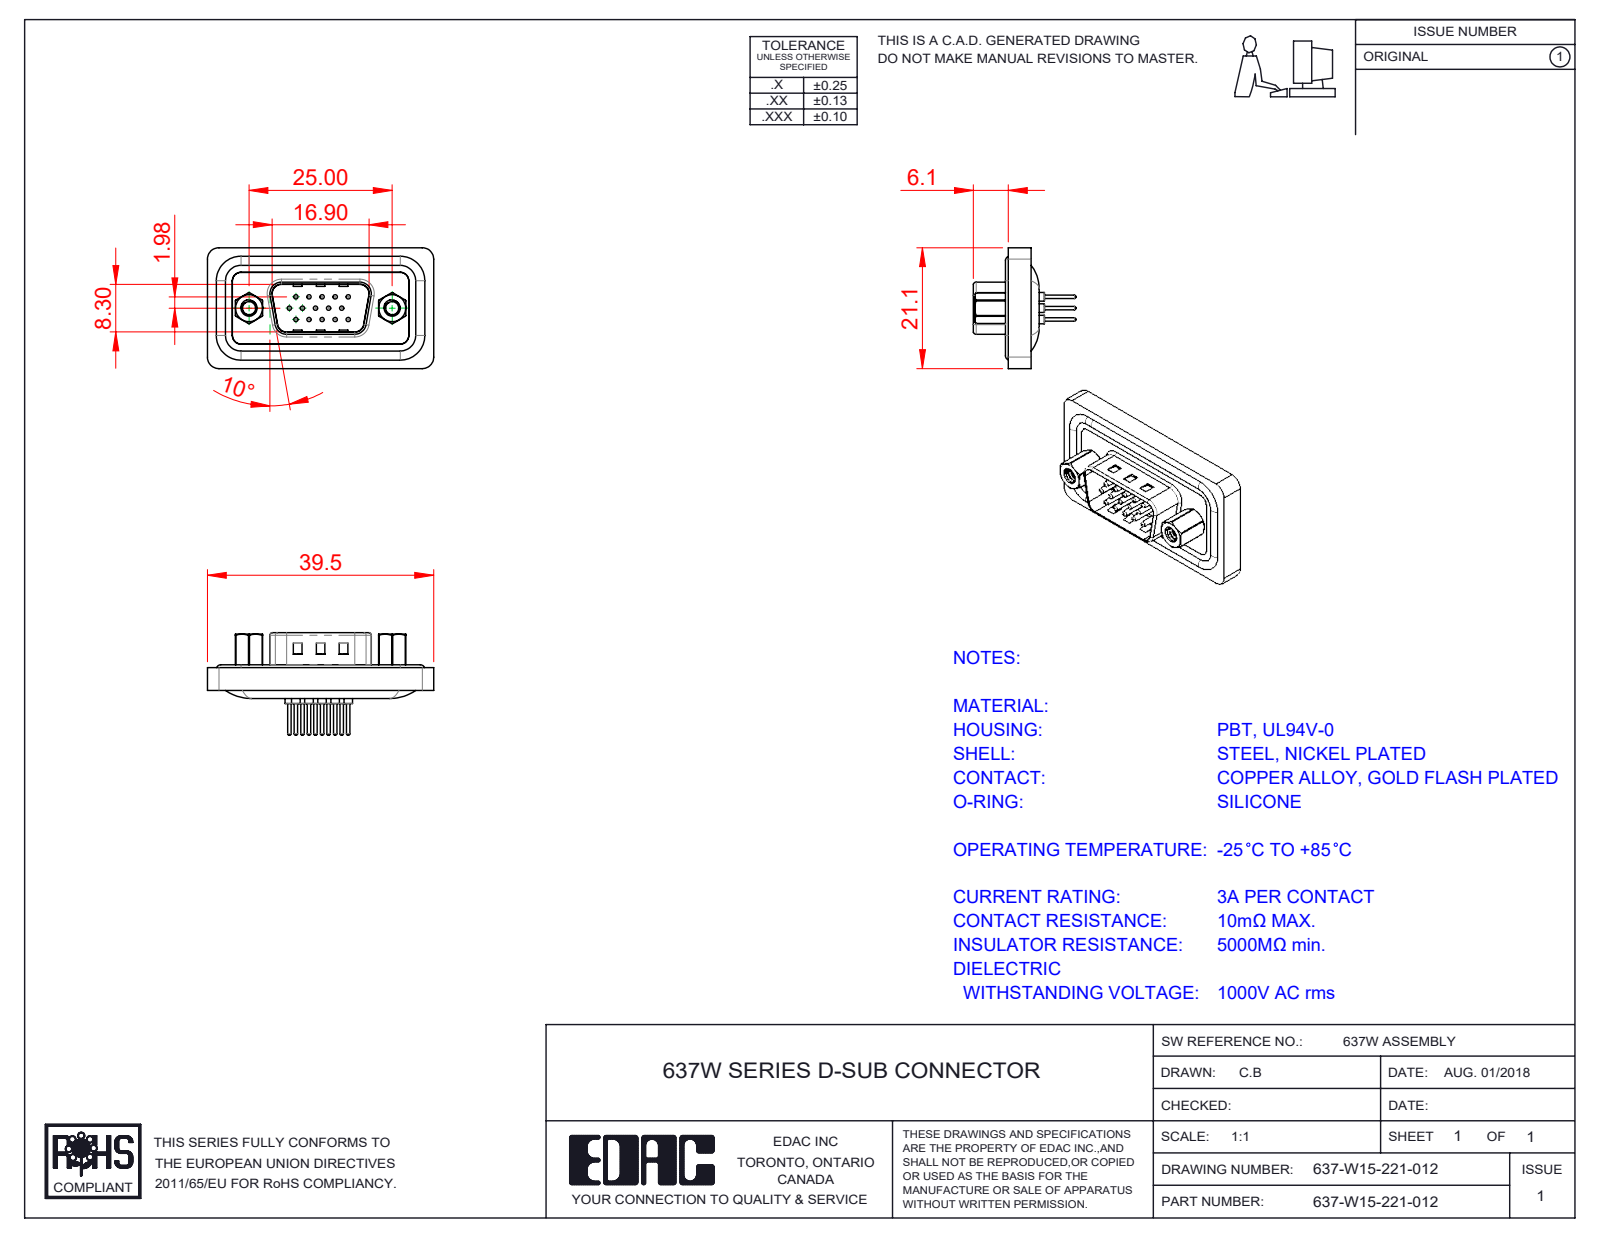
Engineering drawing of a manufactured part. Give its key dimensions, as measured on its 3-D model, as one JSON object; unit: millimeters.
{"part_name": "637W Contact Row 2_21; 637W Waterproof Housing_15 Contacts; 637W Contact Row 3_21; 637W Housing_15 Contacts (+5 more)", "step_written_by": "SolidWorks 2023 (CONFIG_CONTROL_DESIGN)", "units": "millimeters", "bodies": {"solids": 23, "faces": 1033, "planar": 246, "cylindrical": 452, "other": 335}, "overall_size": [39.51, 21.1, 18.1], "volume_mm3": 3988, "surface_area_mm2": 6804, "round_holes": [[0.75, 15], [1.5, 15], [1.6, 15], [2, 15], [2.26, 2], [2.29, 2], [4, 2], [4.8, 2], [5, 2]], "round_bosses_or_shafts": [[0.6, 15], [1.5, 8], [1.6, 4], [4.9, 2], [2.79, 2], [5, 1]], "partial_cylinders_radius": [[1.5, 14], [2, 14], [0.5, 8], [2.7, 6], [0.9, 4], [1.6, 4], [4.3, 4], [0.4, 2]], "face_to_face_distances": [0.4, 1.6, 1.1, 2.9, 2.5, 0.5, 4, 3.6, 3.4, 0.7], "hole_center_spacings": [3.96, 2.28, 4.57, 2.29, 6.05, 6.04, 7.92, 6.86]}
